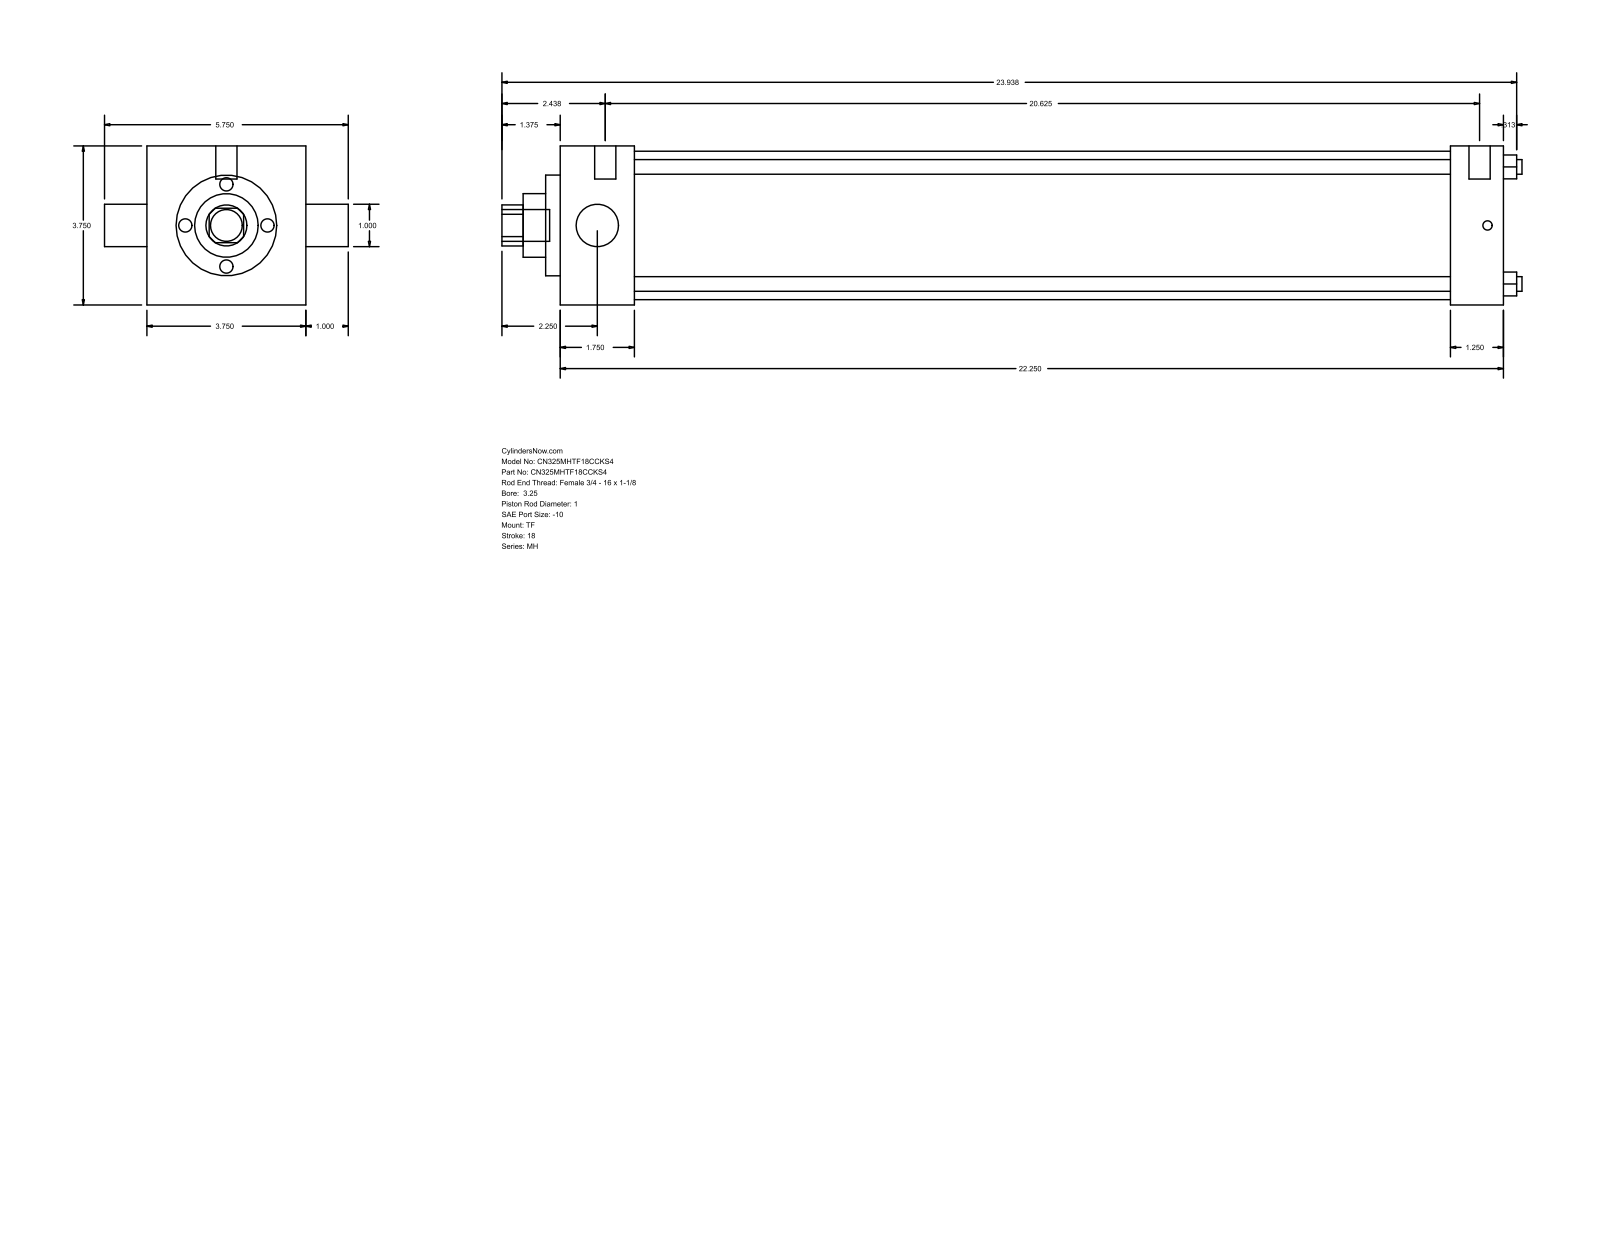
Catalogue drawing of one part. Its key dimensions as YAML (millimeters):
part_name: "MH_TF__0325_1"
step_written_by: "GSSL Pune (CONFIG_CONTROL_DESIGN)"
units: millimeters
bodies: {solids: 0, faces: 86, planar: 61, cylindrical: 25, other: 0}
overall_size: [611.19, 146.05, 95.25]
round_holes:
  - {diameter: 8.76, count: 4}
  - {diameter: 25.4, count: 2}
  - {diameter: 38.1, count: 1}
  - {diameter: 60.33, count: 1}
  - {diameter: 88.9, count: 1}
round_bosses_or_shafts:
  - {diameter: 5.56, count: 3}
  - {diameter: 12.7, count: 2}
  - {diameter: 19.05, count: 1}
partial_cylinders:
  - {radius: 12.29, count: 1}
face_to_face_distances: [95.24, 565.16, 44.46, 533.41, 488.95, 520.7, 31.75, 8.73, 53.19, 542.14]
hole_center_spacings: [49.57, 70.1, 99.14]
